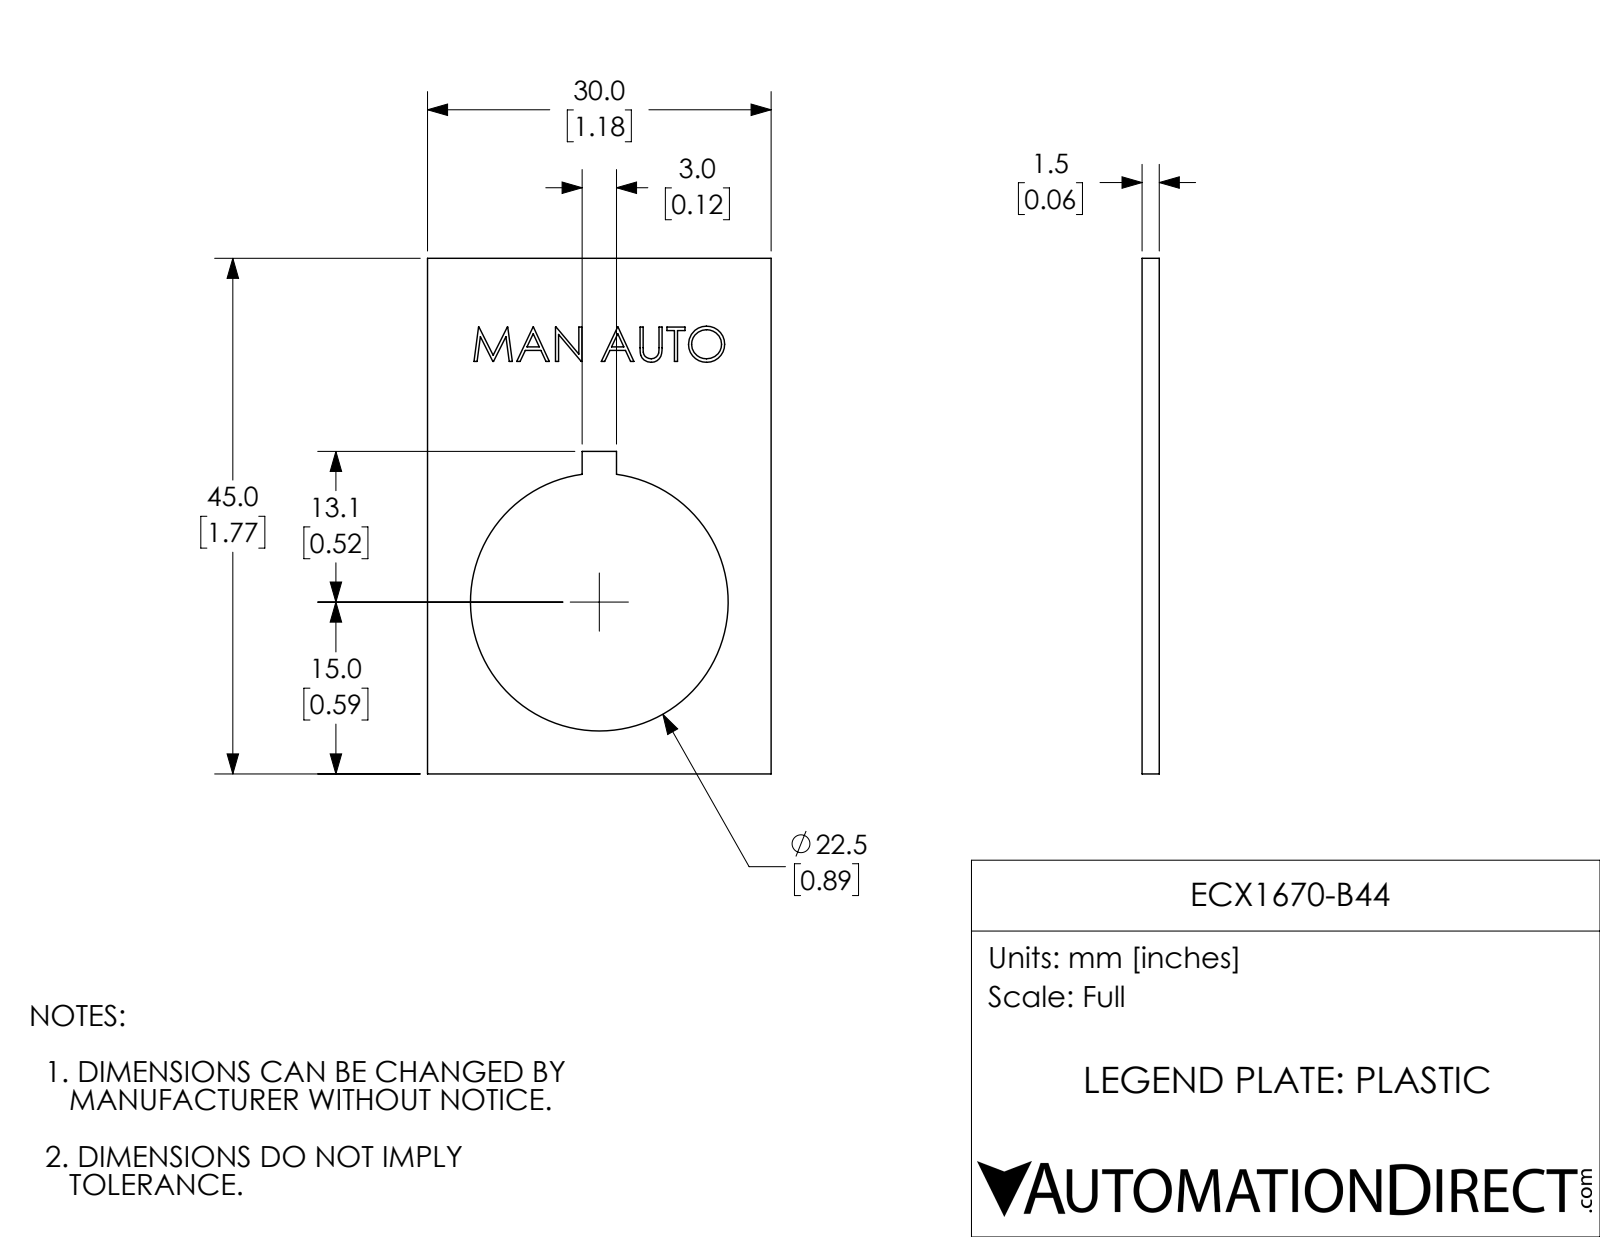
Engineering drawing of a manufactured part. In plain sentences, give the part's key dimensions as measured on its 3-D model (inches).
The part is named "ECX1670-B44". Its 3-D file was written by "SolidWorks 2017 (AUTOMOTIVE_DESIGN)". It is 1 solid with 96 faces: 78 planar, 3 cylindrical and 15 other. Overall it measures 1.772 by 1.181 by 0.059 inches. Its volume is 0.087 cubic inches and its surface area 3.461 square inches. Round holes: 1 of diameter 0.886. The main face-to-face distances are 0.059, 1.181, 1.772, 0.058, 0.531, 0.65, 1.108, 0.663, 0.118, 0.21.
